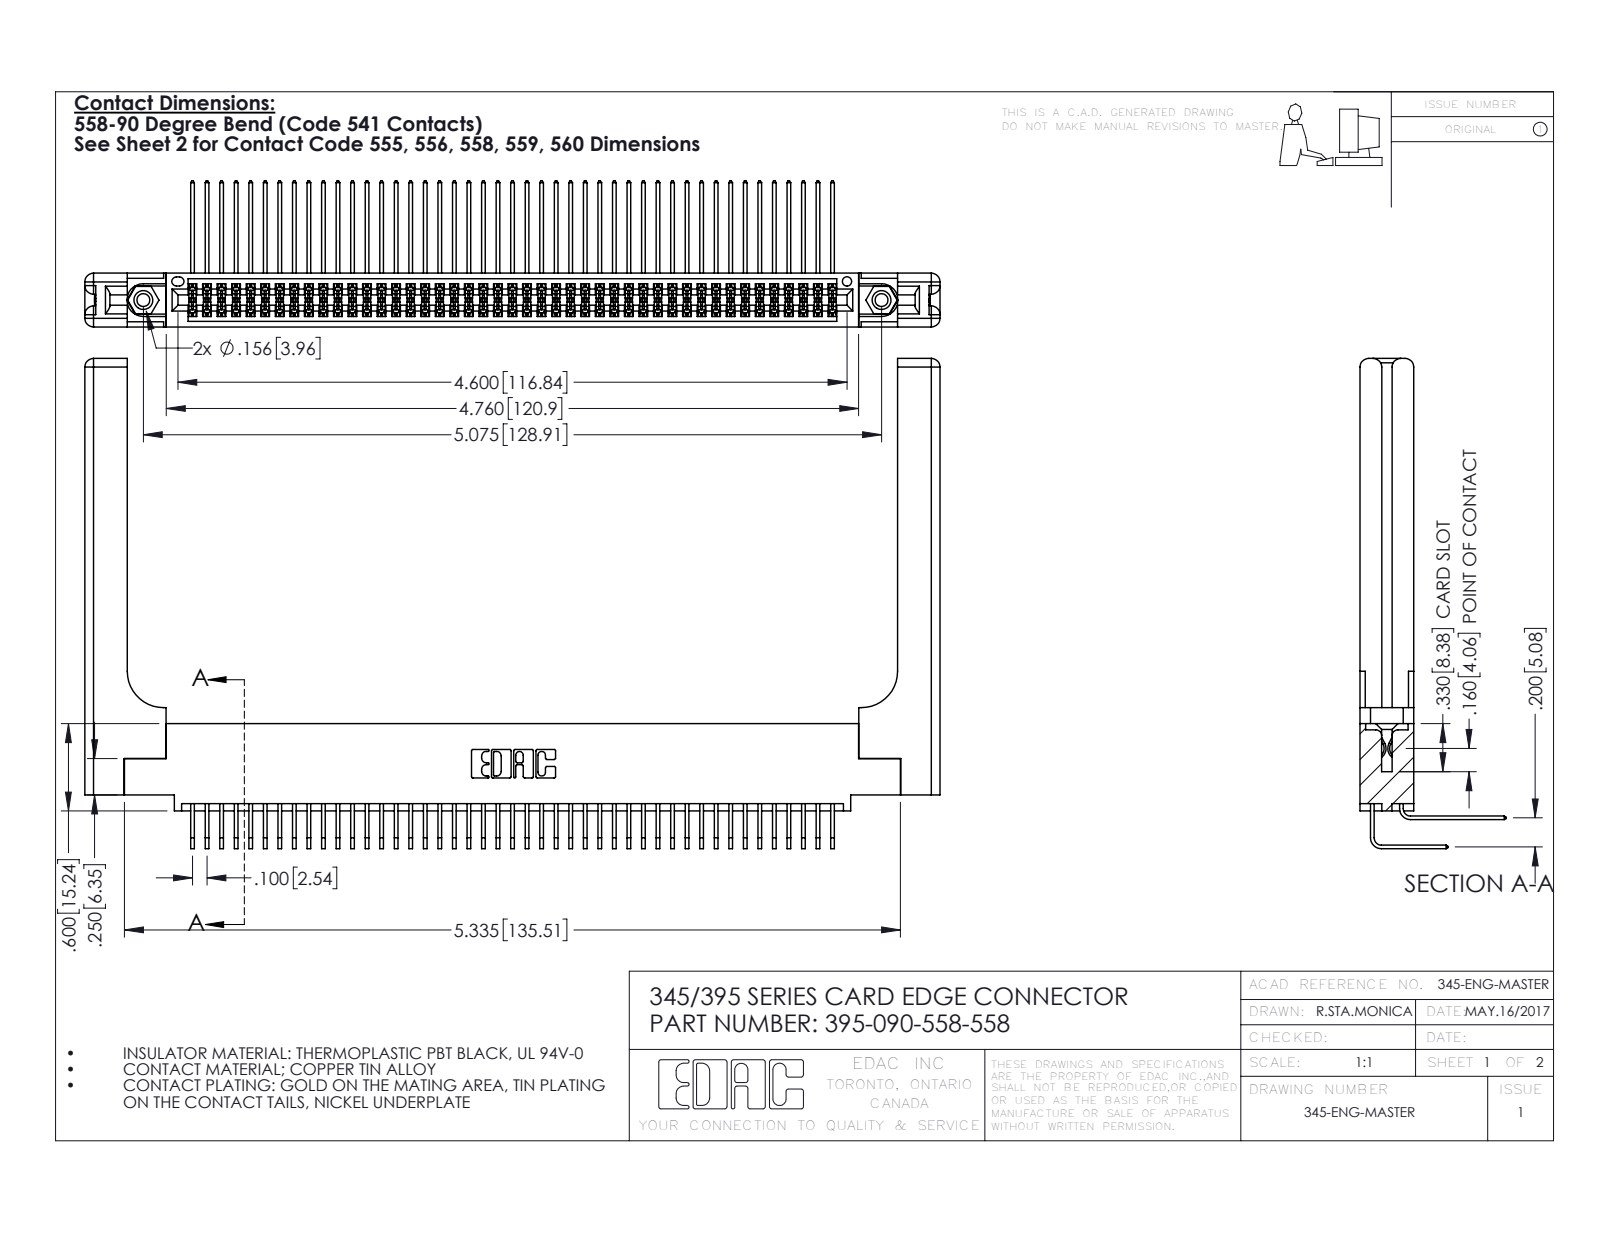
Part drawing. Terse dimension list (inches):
name: 345-220-058_345-220-058; 345-250-001_345-250-001-102; 345-292-001_558 559 Tail - 1; 345-292-001_558 Tail - 2 (+2 more)
written by: SolidWorks 2016 (CONFIG_CONTROL_DESIGN)
unit: in
bodies: 95 solids, 5066 faces (3382 planar, 1624 cylindrical, 60 other)
size: 5.879 × 3.369 × 1.005
volume: 1.431 in³; area: 46.18 in²
holes: 2× ⌀0.089, 2× ⌀0.125, 2× ⌀0.156, 1× ⌀0.064
bosses: 2× ⌀0.155
rounds: 136× R0.006, 22× R0.01, 16× R0.06, 6× R0.007, 6× R0.031, 3× R0.026, 2× R0.014, 2× R0.019
face distances: 0.072, 0.298, 0.37, 0.2, 0.098, 0.272, 0.025, 0.225, 0.148, 0.15
hole spacings: 0.27, 4.839, 5.075
